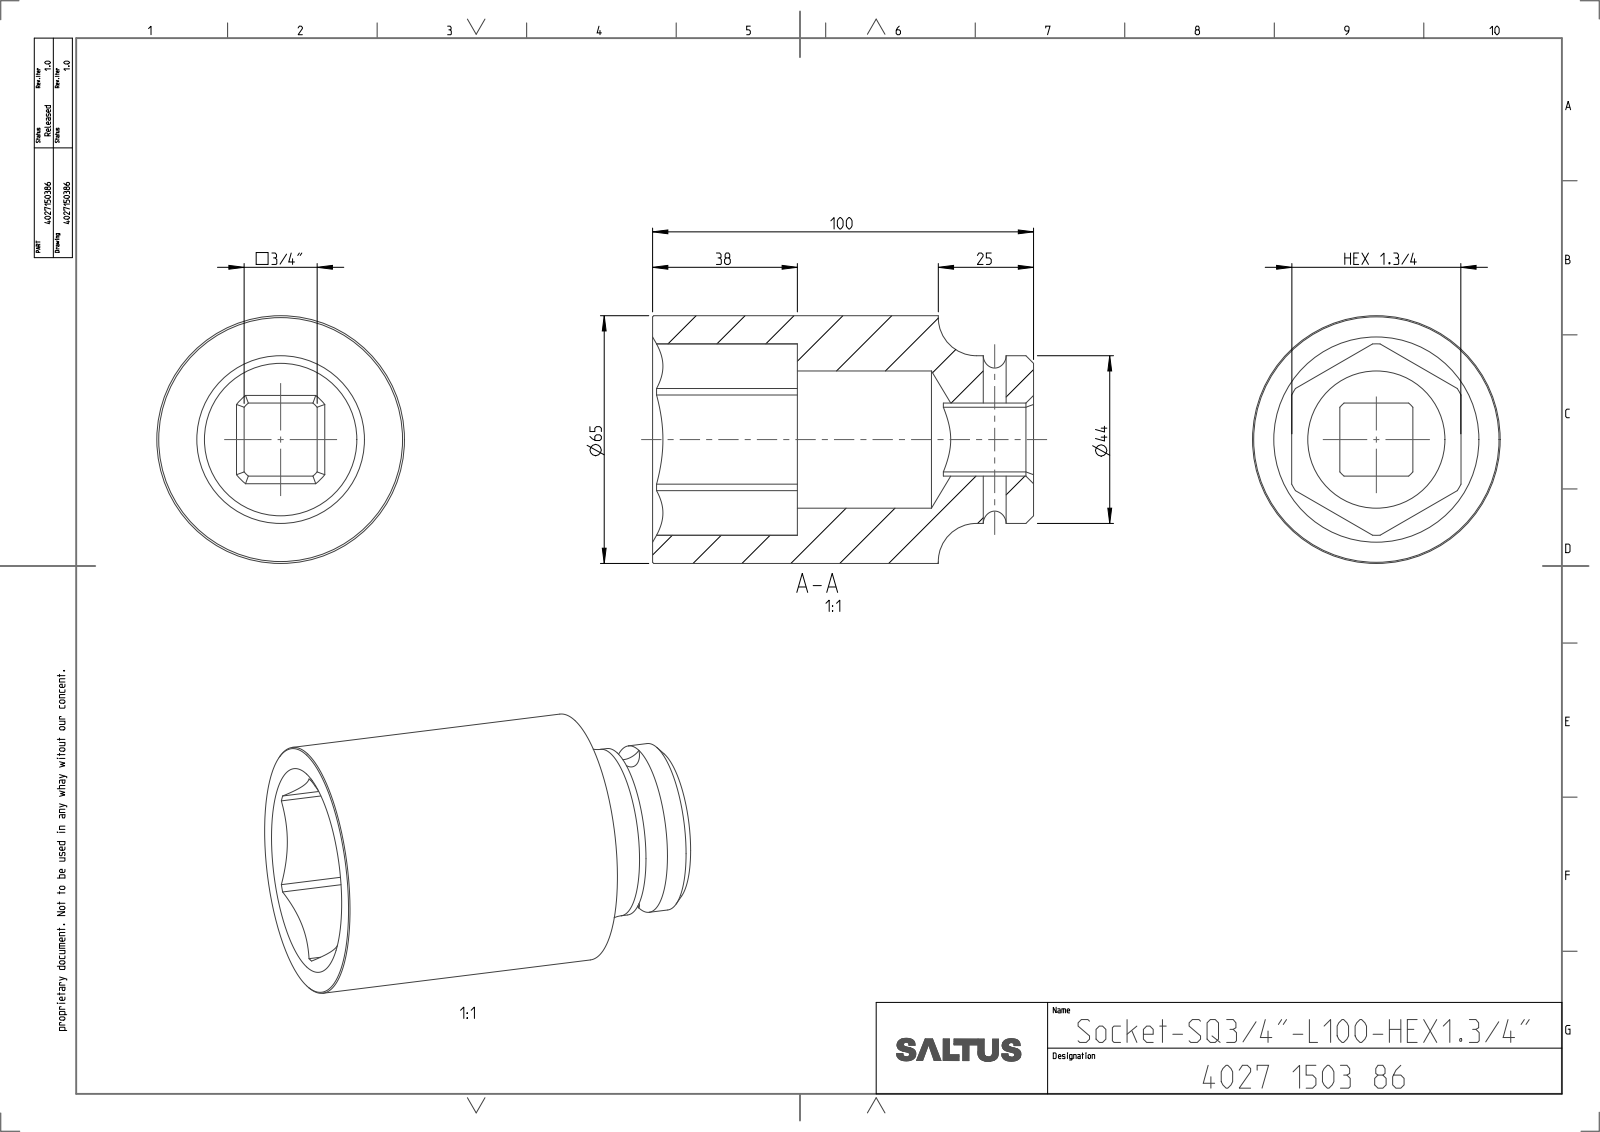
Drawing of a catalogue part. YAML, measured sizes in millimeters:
part_name: "4027150386"
step_written_by: "CREO PARAMETRIC BY PTC INC, 2022414 (CONFIG_CONTROL_DESIGN)"
units: millimeters
bodies: {solids: 1, faces: 56, planar: 18, cylindrical: 22, other: 16}
overall_size: [100, 65, 65]
volume: 174869
surface_area: 35784
round_holes:
  - {diameter: 6, count: 1}
  - {diameter: 36, count: 1}
round_bosses_or_shafts:
  - {diameter: 65, count: 1}
  - {diameter: 44, count: 1}
partial_cylinders:
  - {radius: 12.8, count: 1}
  - {radius: 25.11, count: 1}
face_to_face_distances: [44.44, 44.46, 100, 12.64, 31.82, 62, 38, 19.18, 25, 37]
